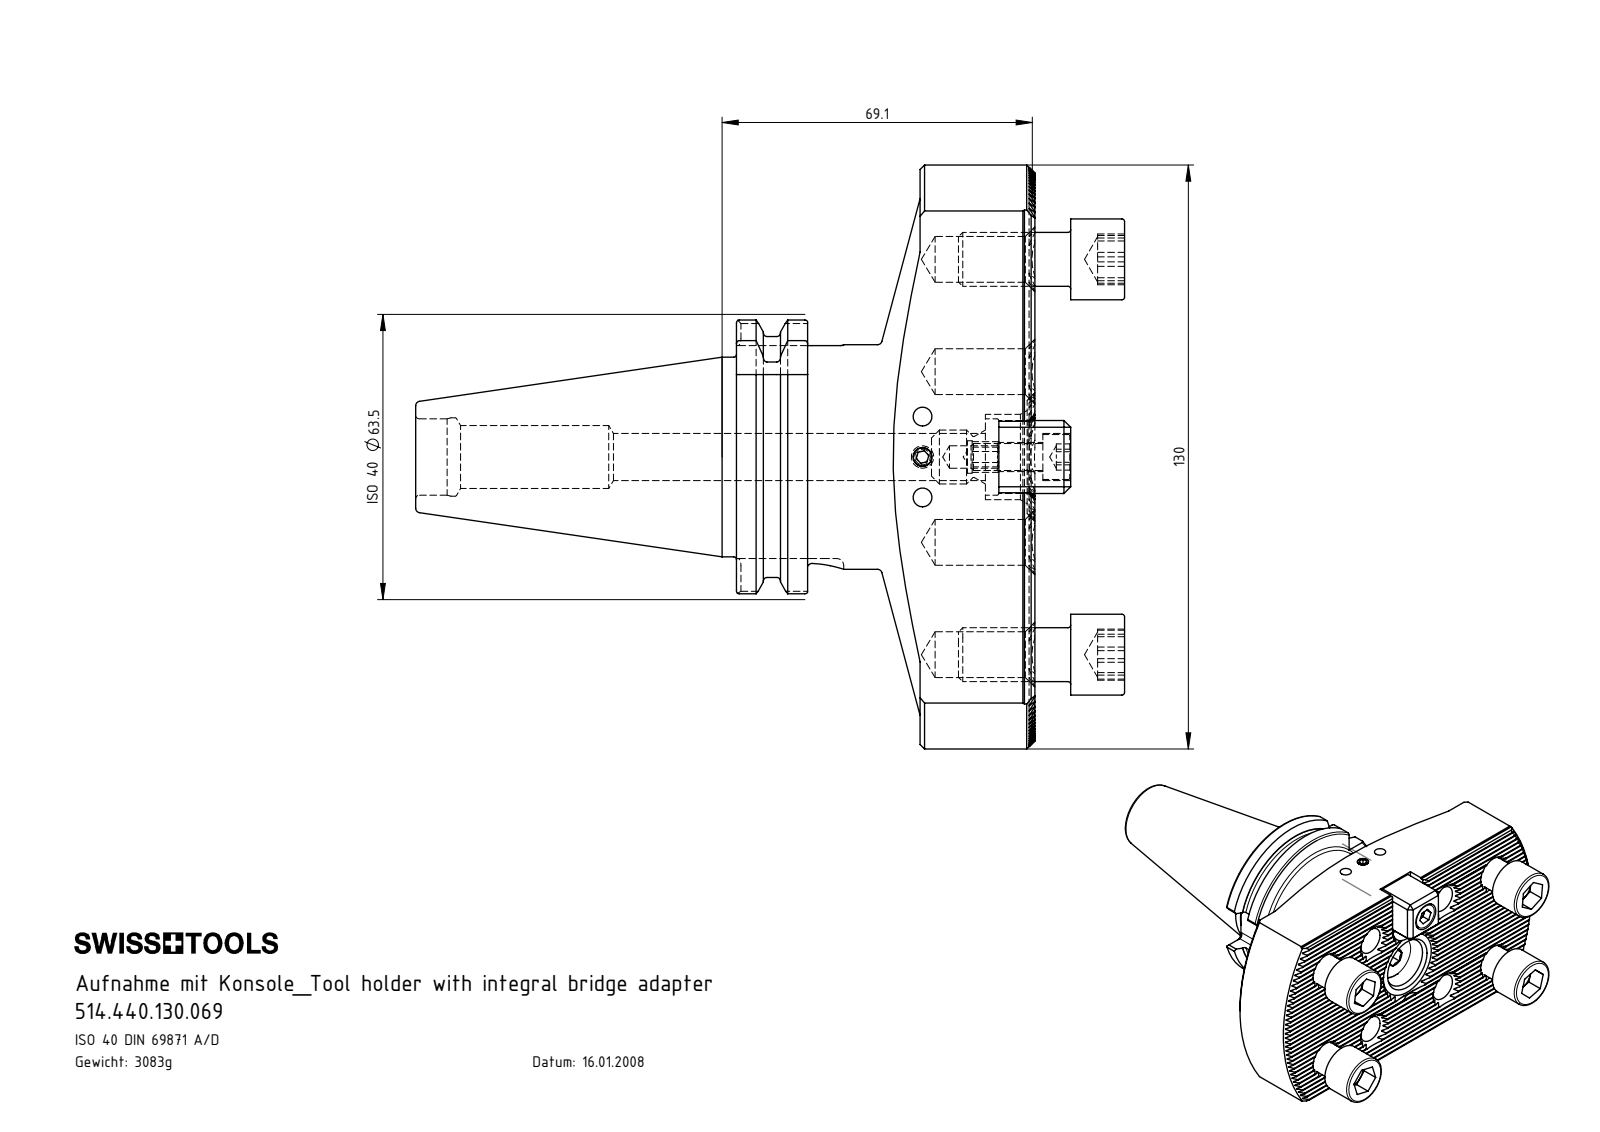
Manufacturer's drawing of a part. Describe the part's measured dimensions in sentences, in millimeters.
The part is named "ISO 4762 M6 x 16; ISO 4762 M12 x 25; DIN 908 - M12x1.5; ISO 4026 - M5 x 8 (+3 more)". Its 3-D file was written by "SolidWorks 2017 (CONFIG_CONTROL_DESIGN)". It is 10 solids with 886 faces: 502 planar, 210 cylindrical and 174 other. Overall it measures 157.9 by 130 by 70 millimeters. Its volume is 392 696 cubic millimeters and its surface area 72 489 square millimeters. Round holes: 8 of diameter 10.2, 3 of diameter 4.2, 2 of diameter 10.5, 1 of diameter 5, 1 of diameter 6.5, 1 of diameter 7.24, 1 of diameter 14, 1 of diameter 17, 1 of diameter 17.45, 1 of diameter 19. Round bosses or shafts: 5 of diameter 12, 4 of diameter 18, 1 of diameter 50, 1 of diameter 44.45, 1 of diameter 10, 1 of diameter 6, 1 of diameter 5. Partial cylindrical surfaces (rounded edges, fillets, slot ends): 34 of radius 0.14, 8 of radius 1.6, 1 of radius 7.95, 1 of radius 8, 1 of radius 8.05, 1 of radius 28, 1 of radius 31.75, 1 of radius 65. The main face-to-face distances are 1.73, 17.32, 70, 8.66, 3.46, 5.2, 6.93, 15.59, 19.05, 3.47. The hole center spacings are 25, 27.59, 40, 47.17, 48.33, 63, 74.63, 9.
